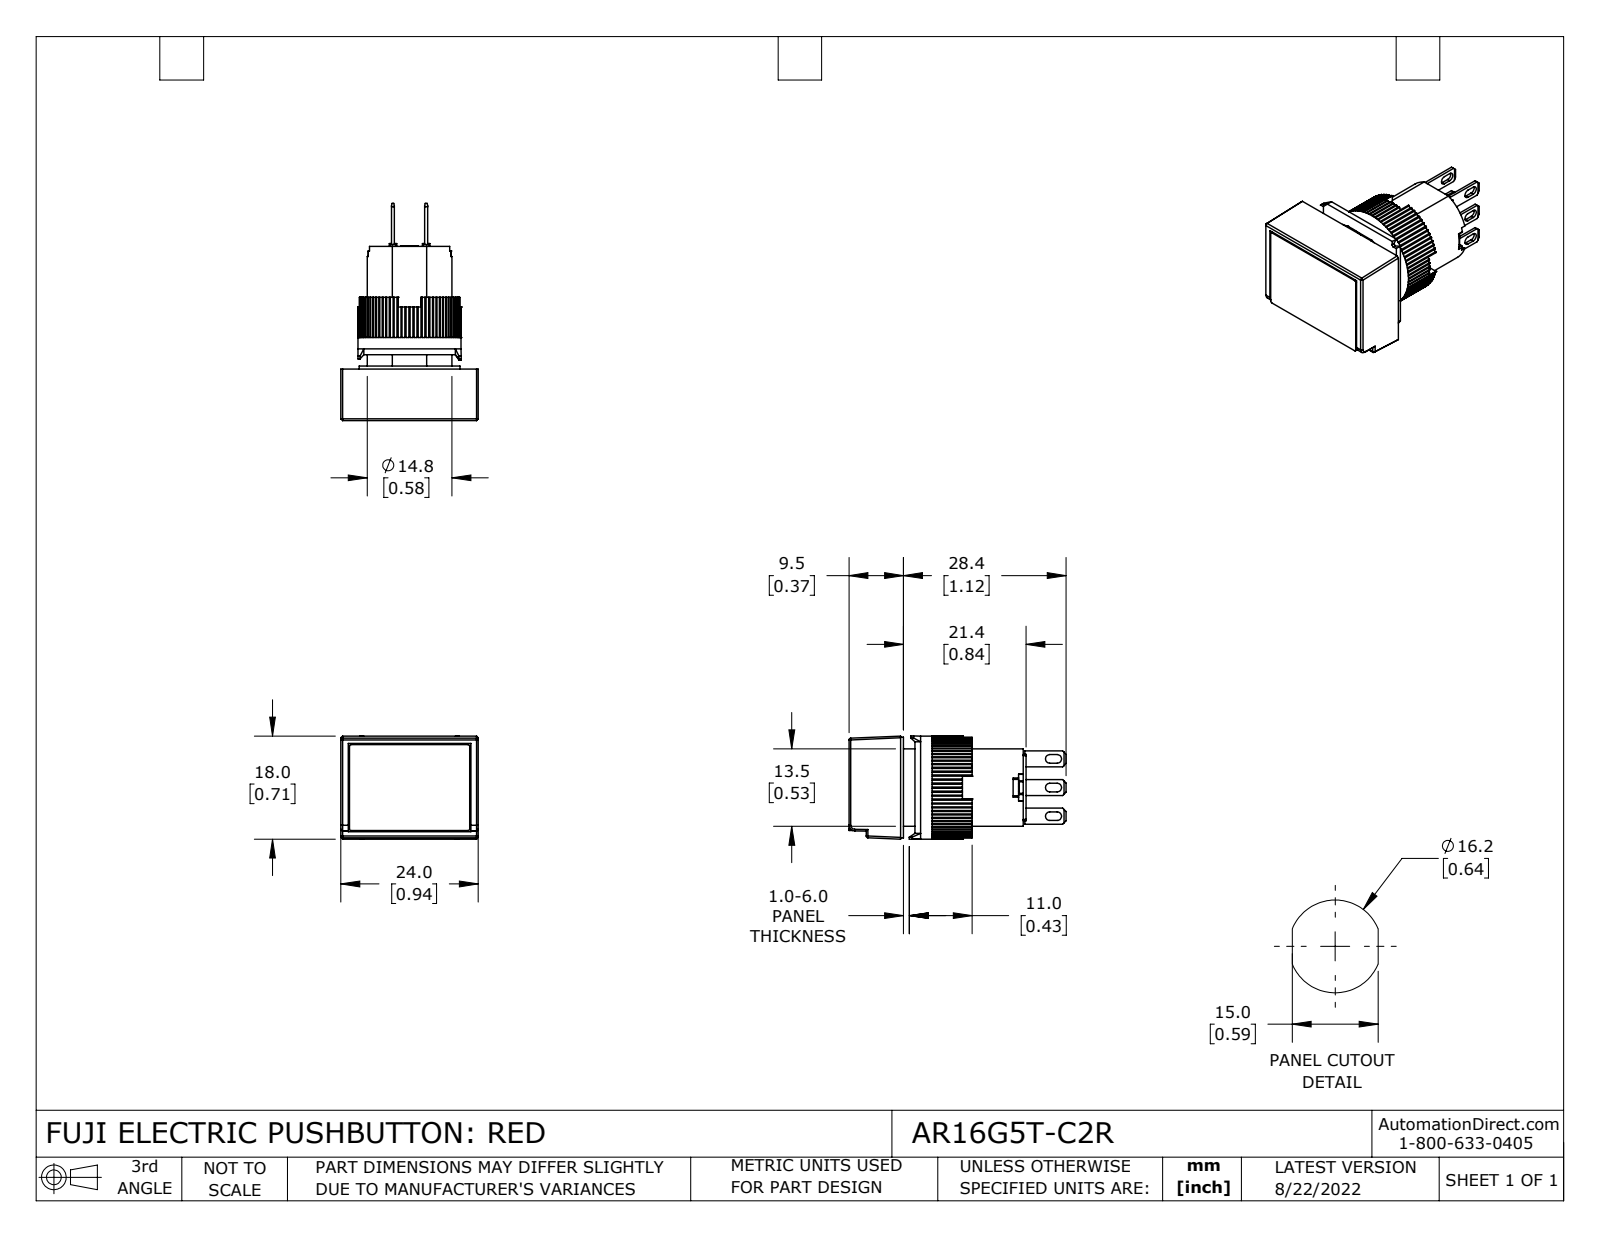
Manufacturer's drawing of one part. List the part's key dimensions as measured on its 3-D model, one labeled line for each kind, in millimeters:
Part name (STEP PRODUCT): AR16G5T-C2R
STEP written by: SolidWorks 2021 (CONFIG_CONTROL_DESIGN)
Units: millimetres
Bodies: 12 solids, 811 faces (630 planar, 175 cylindrical, 6 other)
Overall size (bounding box): 37.9 × 24 × 18
Volume: 7 330 mm³ · Surface area: 6 014 mm²
Round holes (diameter × count): ⌀13.8 ×1, ⌀14.8 ×1
Round bosses / shafts (diameter × count): ⌀18 ×1, ⌀17.6 ×1
Partial cylindrical surfaces — rounded edges, fillets, slot ends (radius × count): R0.3 ×80, R0.2 ×12, R0.3 ×6, R0.8 ×6, R1 ×1
Main face-to-face distances: 5.4, 9, 3.6, 12.5, 8.9, 3.5, 0.5, 21.4, 1.5, 11.5
